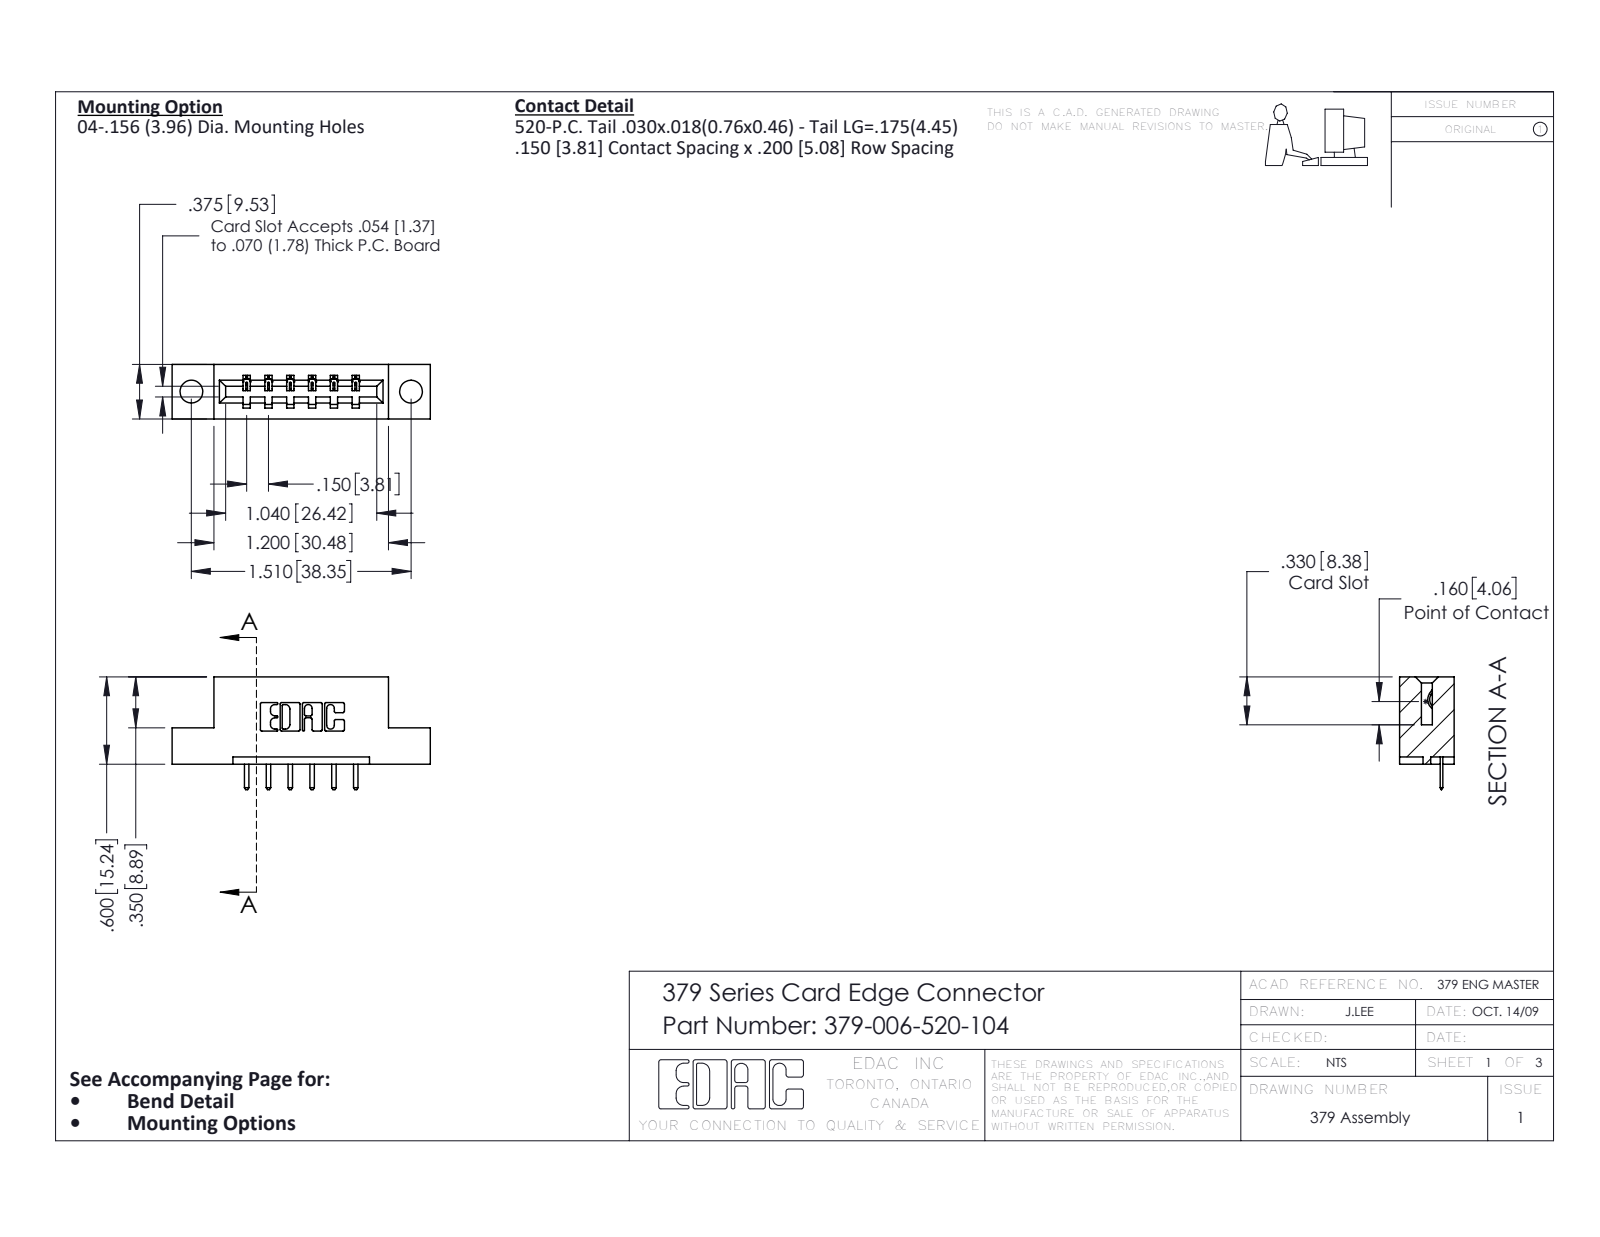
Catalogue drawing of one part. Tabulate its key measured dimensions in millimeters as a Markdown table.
| quantity | value |
| --- | --- |
| part name | 379 Part_Flush - .156 Dia - TH; 345-292-001_345-293-120; 379-006-520-104 |
| STEP written by | SolidWorks 2016 (CONFIG_CONTROL_DESIGN) |
| units | millimeters |
| bodies | 7 solids, 486 faces (334 planar, 152 cylindrical, 0 other) |
| overall size | 45.1 × 19.7 × 9.5 |
| volume | 4 200 mm³ |
| surface area | 3 853 mm² |
| round holes (diameter × count) | 4 × 2 |
| partial cylindrical surfaces (radius × count) | 0.3 × 22, 0.3 × 14, 0.2 × 12, 0.2 × 6, 0.8 × 6, 0.7 × 3, 0.4 × 1, 0.6 × 1 |
| main face-to-face distances | 7.6, 5.1, 9.5, 1.3, 3.8, 6.4, 8.9, 1.9, 15.2, 14 |
| hole center spacings | 38.4 |
